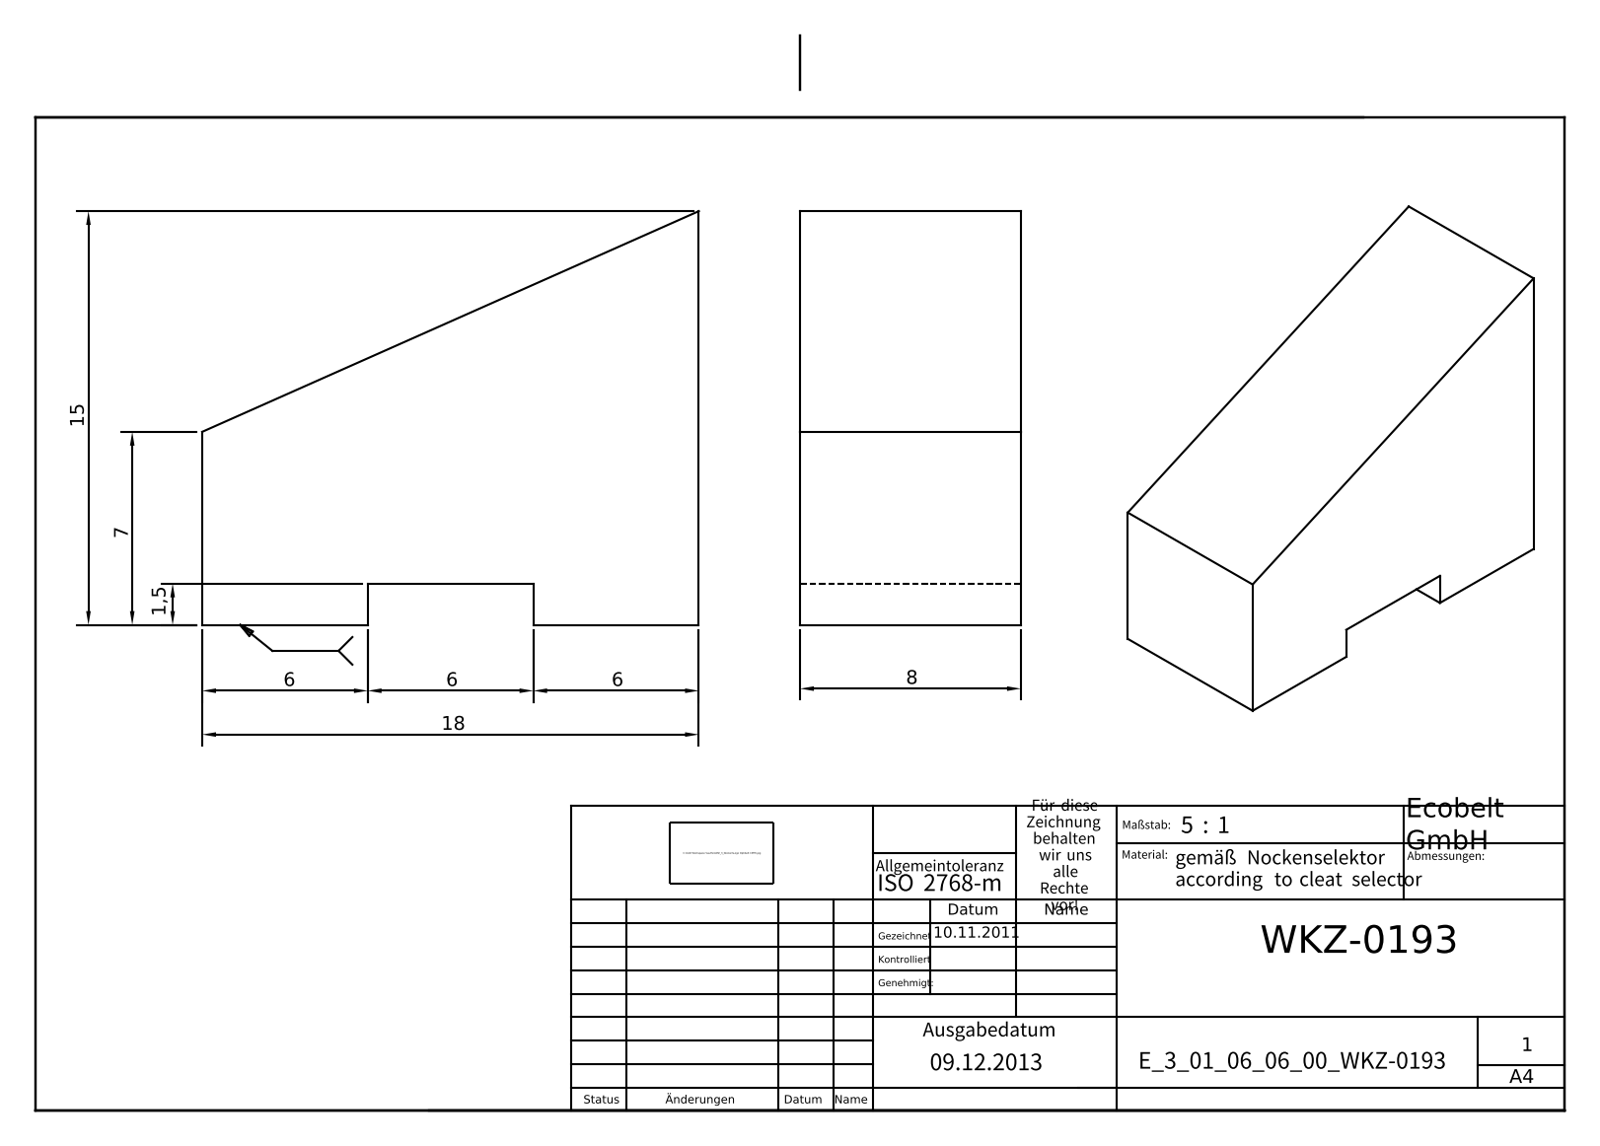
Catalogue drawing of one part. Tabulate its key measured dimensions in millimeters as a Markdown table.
| quantity | value |
| --- | --- |
| part name | E_3_01_06_06_00_WKZ-0193 |
| STEP written by | Autodesk Inventor 2025 (AUTOMOTIVE_DESIGN) |
| units | millimeters |
| bodies | 1 solid, 10 faces (10 planar, 0 cylindrical, 0 other) |
| overall size | 18 × 15 × 8 |
| volume | 1 512 mm³ |
| surface area | 880 mm² |
| main face-to-face distances | 8, 18, 1.5, 6, 12 |
